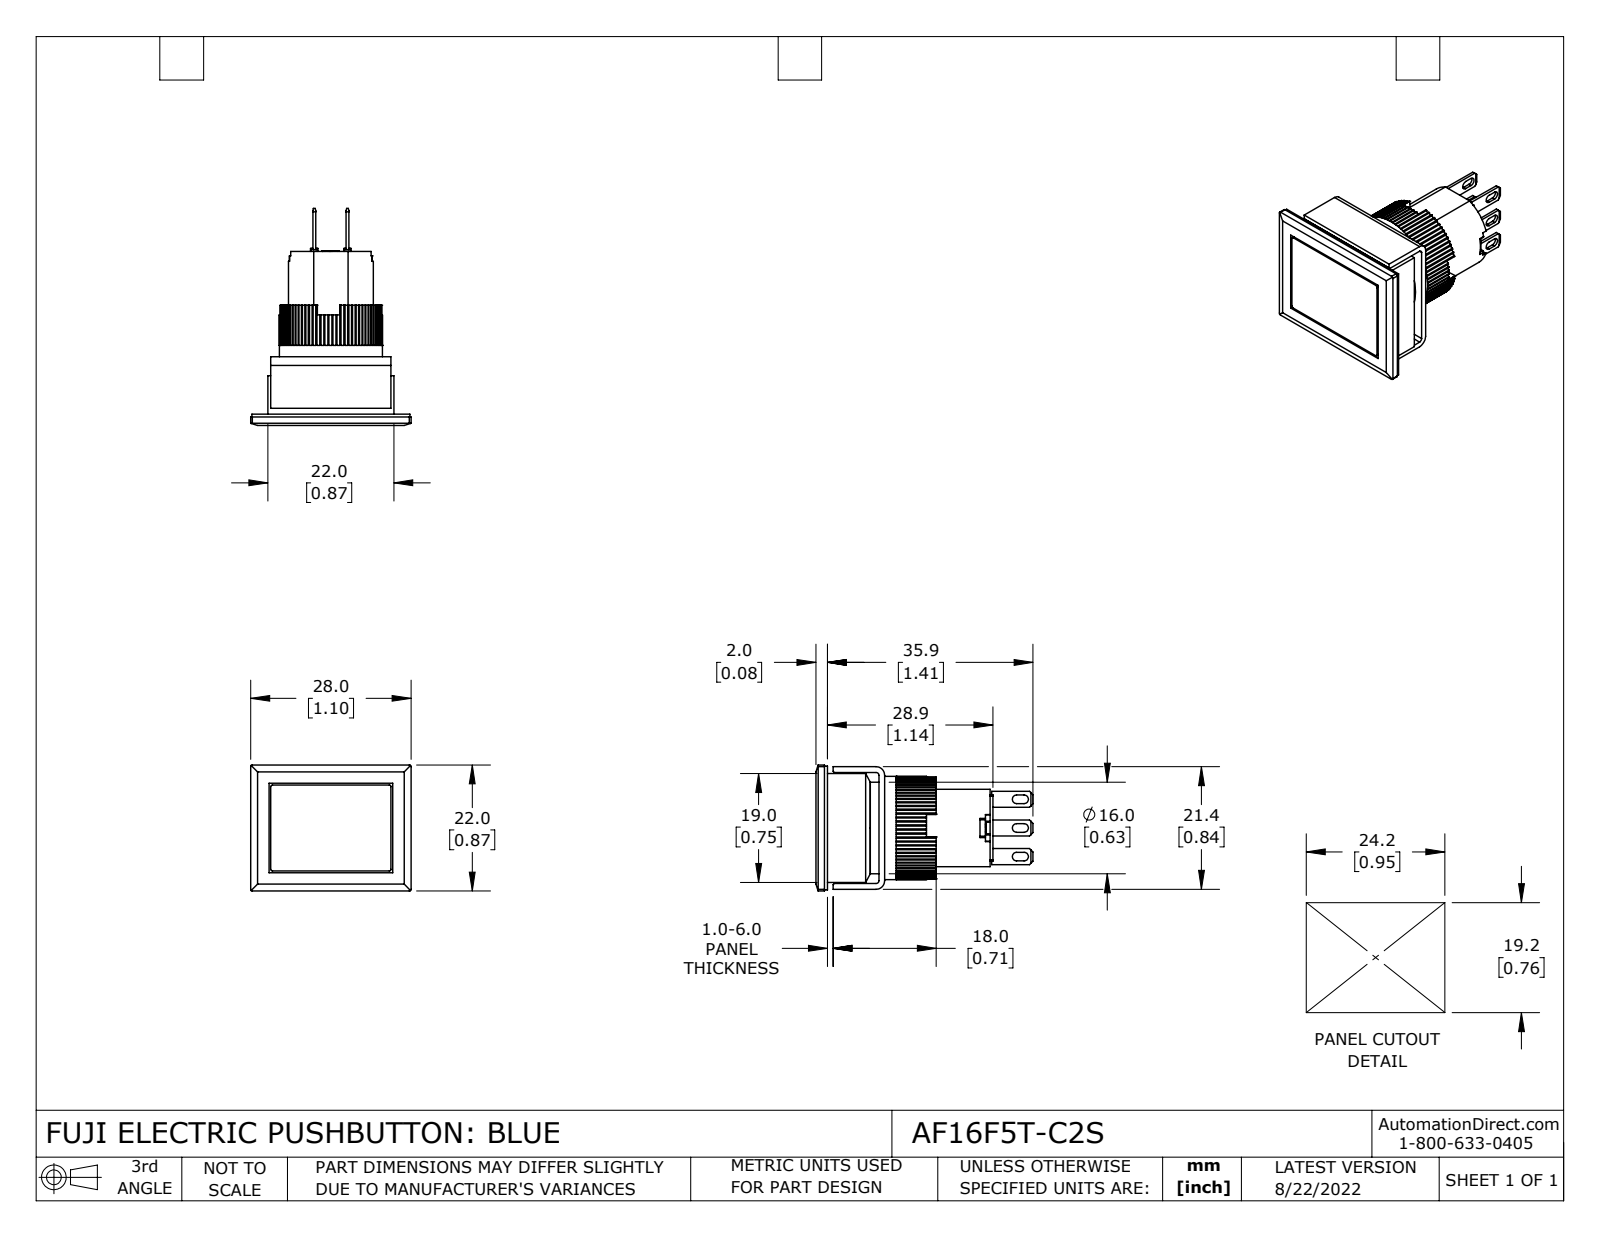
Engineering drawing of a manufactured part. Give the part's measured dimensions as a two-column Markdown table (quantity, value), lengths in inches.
| quantity | value |
| --- | --- |
| part name | AF16F5T-C2S |
| STEP written by | SolidWorks 2021 (CONFIG_CONTROL_DESIGN) |
| units | inches |
| bodies | 12 solids, 798 faces (620 planar, 176 cylindrical, 2 other) |
| overall size | 1.492 × 1.102 × 0.866 |
| volume | 0.541 in³ |
| surface area | 11.85 in² |
| round holes (diameter × count) | 0.039 × 1, 0.709 × 1 |
| round bosses / shafts (diameter × count) | 0.63 × 1, 0.583 × 1 |
| partial cylindrical surfaces (radius × count) | 0.01 × 80, 0.008 × 12, 0.012 × 8, 0.03 × 6, 0.02 × 2, 0.059 × 2 |
| main face-to-face distances | 0.374, 0.059, 0.02, 0.142, 0.039, 0.315, 0.232, 0.083, 0.079, 0.756 |
